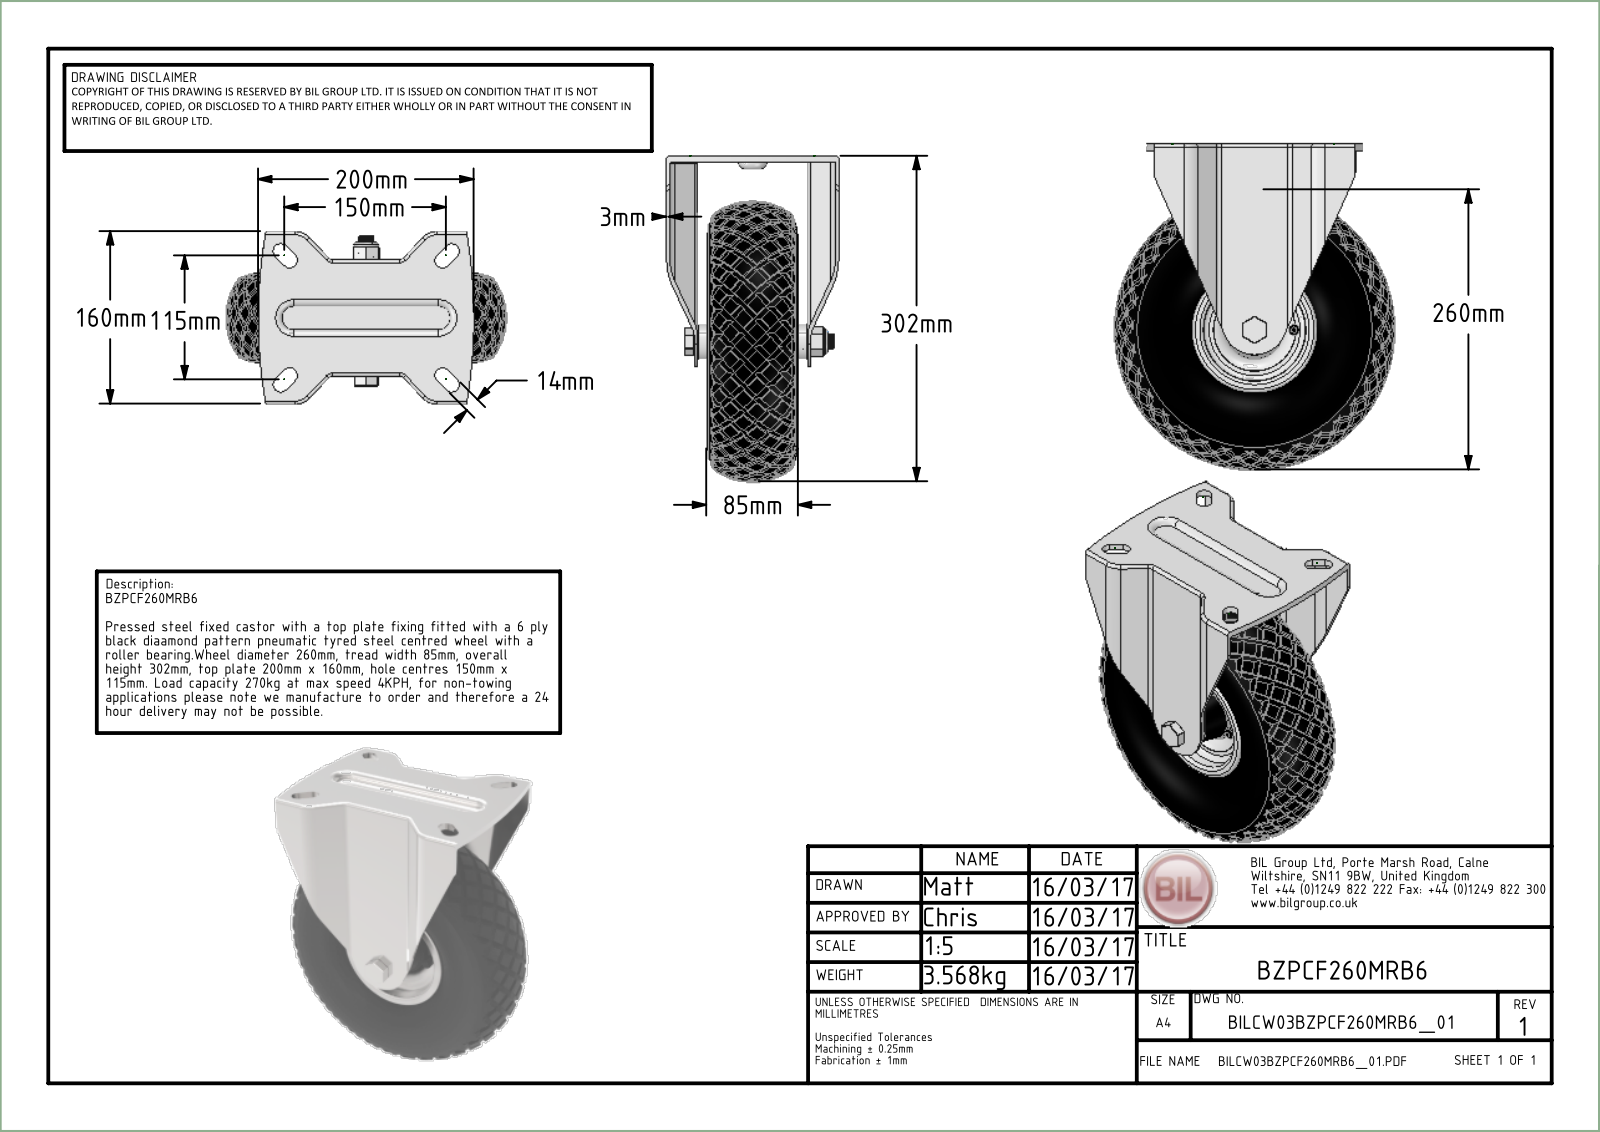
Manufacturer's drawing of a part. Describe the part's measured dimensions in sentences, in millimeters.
The part is named "BZPCF260MRB6 v4; BZPCF260AS - 101 v1; BZPCF260AS v1 (1); BZPCF260AS (1) (+8 more)". Its 3-D file was written by "Autodesk Translation Framework v13.20.0.188 (AP242_MANAGED_MODEL_BASED_3D_ENGINEERING_MIM_LF)". It is 24 solids with 2586 faces: 196 planar, 257 cylindrical and 2133 other. Overall it measures 307 by 260 by 160 millimeters. Its volume is 3 306 000 cubic millimeters and its surface area 699 356 square millimeters. Round holes: 1 of diameter 9, 1 of diameter 14, 1 of diameter 14.2, 1 of diameter 15.2, 1 of diameter 16, 1 of diameter 20, 1 of diameter 21, 1 of diameter 35, 1 of diameter 111, 1 of diameter 114, 1 of diameter 182, 1 of diameter 186. Round bosses or shafts: 11 of diameter 7.5, 1 of diameter 187.2, 1 of diameter 184, 1 of diameter 61.5, 1 of diameter 58, 1 of diameter 34, 1 of diameter 32.5, 1 of diameter 32. Partial cylindrical surfaces (rounded edges, fillets, slot ends): 10 of radius 1.5, 10 of radius 3, 8 of radius 1, 8 of radius 7.05, 6 of radius 0.5, 6 of radius 4, 4 of radius 0.47, 4 of radius 0.9. The main face-to-face distances are 3, 104, 38.16, 8, 11, 96, 93, 101, 107, 41.16. The hole center spacings are 41.78.
